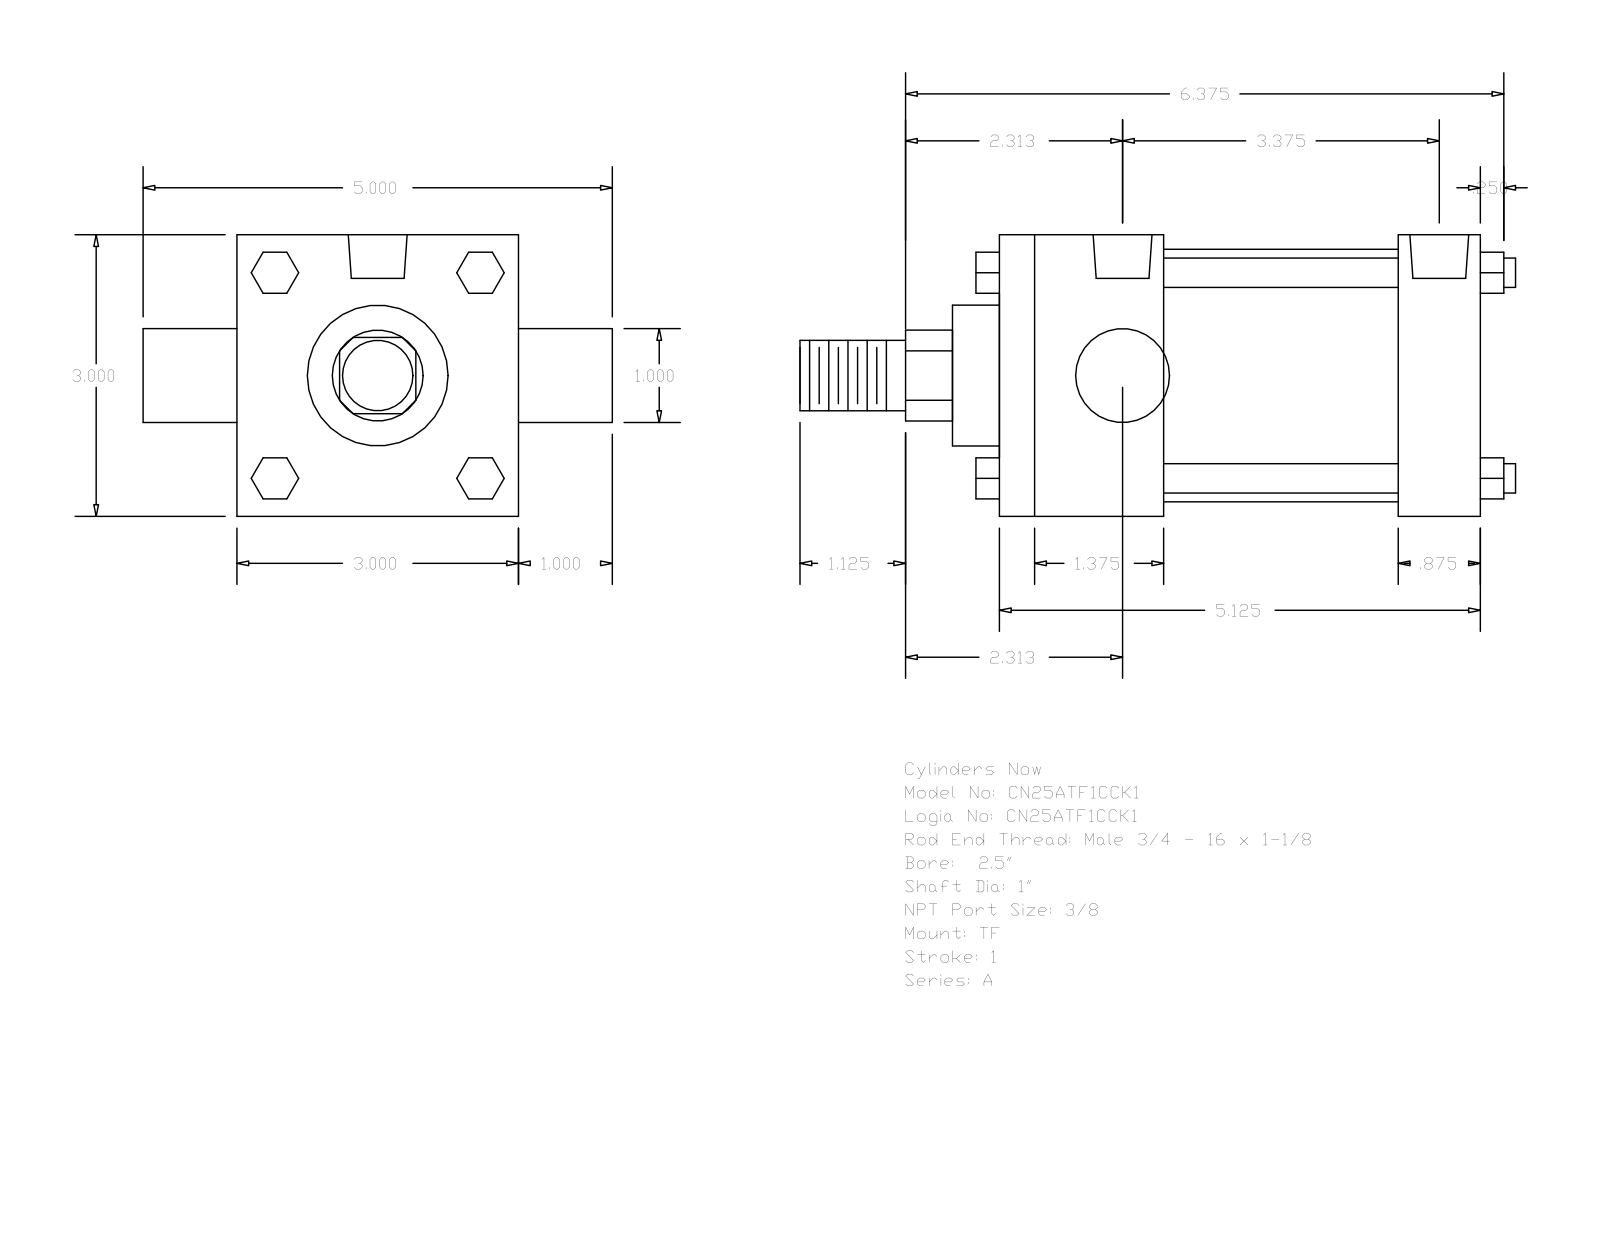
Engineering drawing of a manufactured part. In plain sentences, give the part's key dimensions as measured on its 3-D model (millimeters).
The part is named "A_TF__0250_1". Its 3-D file was written by "GSSL Pune (CONFIG_CONTROL_DESIGN)". It is 0 solids with 120 faces: 92 planar, 28 cylindrical and 0 other. Overall it measures 193.68 by 127 by 76.2 millimeters. Round holes: 3 of diameter 5.56, 2 of diameter 15.93. Round bosses or shafts: 4 of diameter 7.94, 2 of diameter 25.4, 1 of diameter 68.33, 1 of diameter 38.1, 1 of diameter 19.05. Partial cylindrical surfaces (rounded edges, fillets, slot ends): 1 of radius 12.29. The main face-to-face distances are 76.2, 130.17, 44.45, 107.95, 63.5, 85.72, 22.22, 25.4, 101.6, 12.7. The hole center spacings are 2.38, 88.1, 85.72, 90.48.
